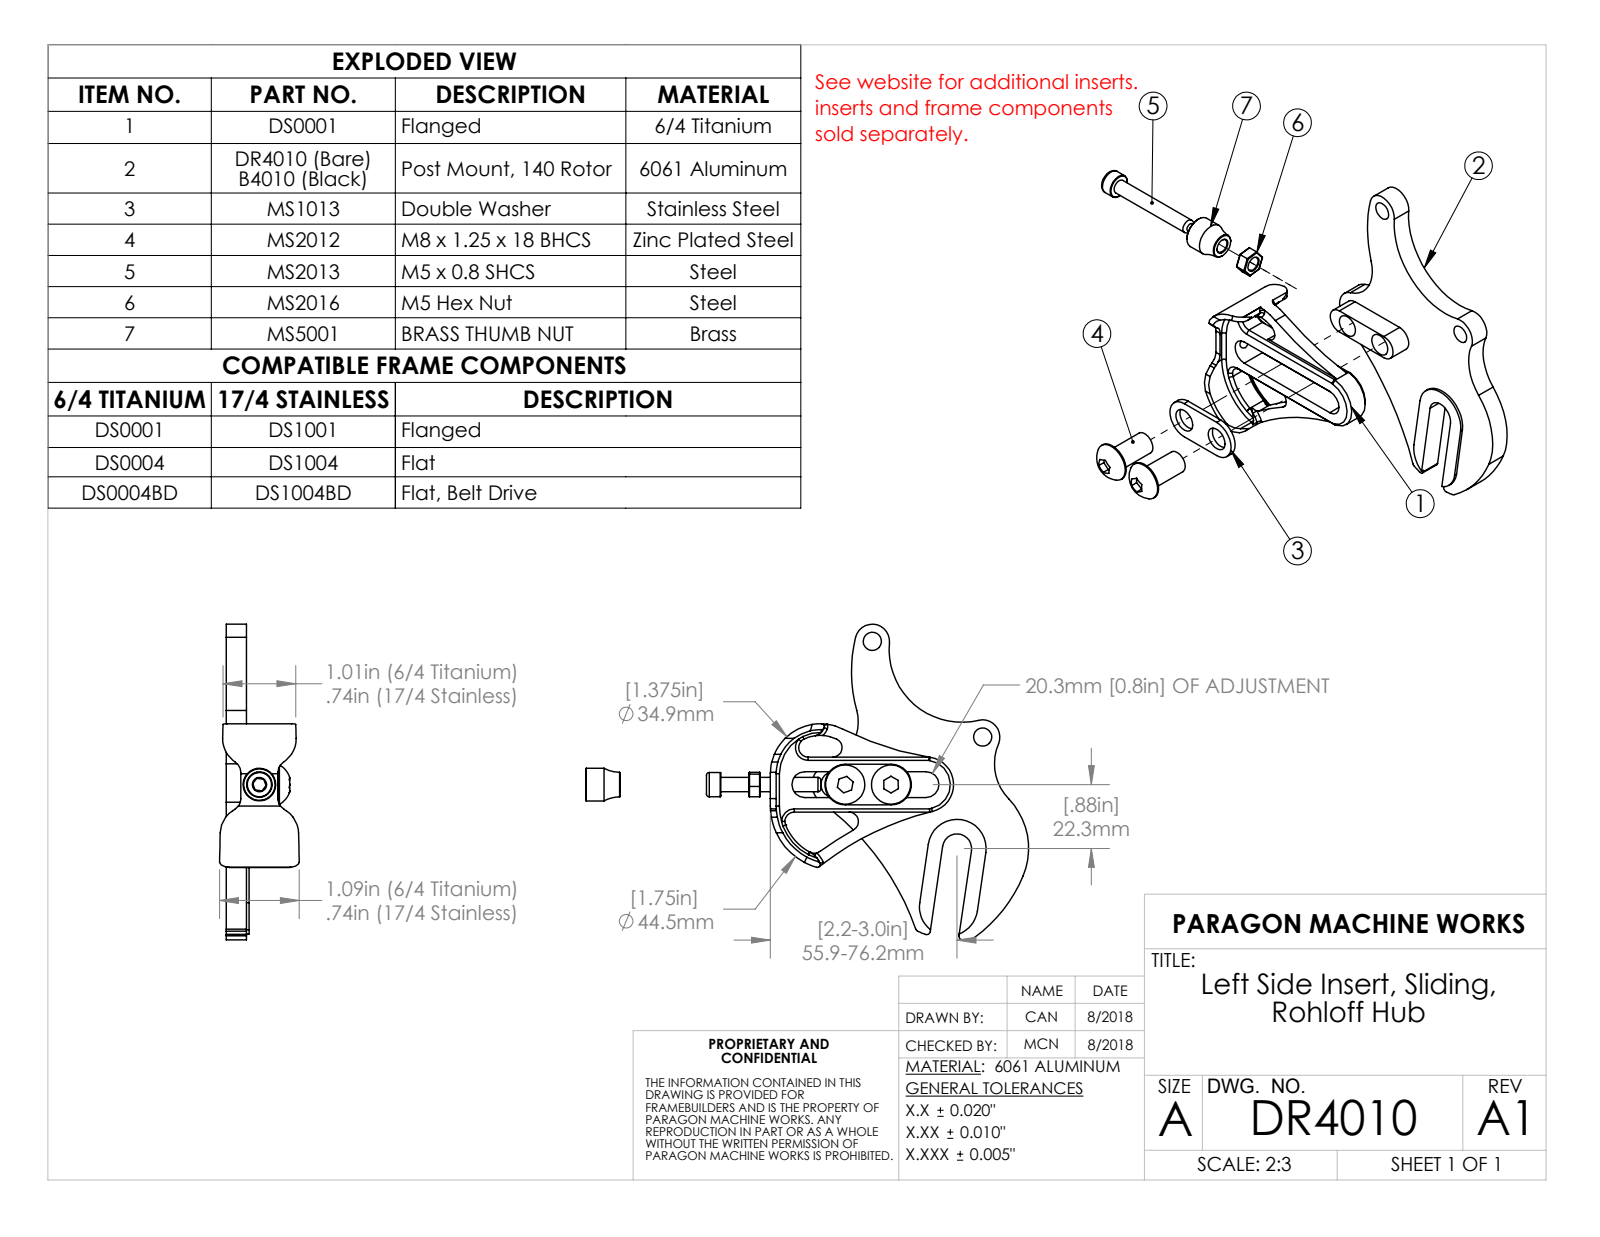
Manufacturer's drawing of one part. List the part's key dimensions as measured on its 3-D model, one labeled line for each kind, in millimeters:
Part name (STEP PRODUCT): DR4010
STEP written by: SolidWorks 2023 (AUTOMOTIVE_DESIGN)
Units: millimetres
Bodies: 1 solid, 45 faces (10 planar, 35 cylindrical, 0 other)
Overall size (bounding box): 102 × 72.1 × 14.9
Volume: 28 970 mm³ · Surface area: 12 040 mm²
Round holes (diameter × count): ⌀6.4 ×2, ⌀7.9 ×2
Partial cylindrical surfaces — rounded edges, fillets, slot ends (radius × count): R1.3 ×3, R4.5 ×2, R6 ×2, R10.2 ×2, R50.8 ×2, R3 ×1, R5.1 ×1, R7.6 ×1
Main face-to-face distances: 7.1, 8, 0.9, 10.2, 9, 14.9, 7.7, 6.8, 8, 2.2
Hole centre spacings: 16, 36, 50.4, 50.8, 50.9, 51
